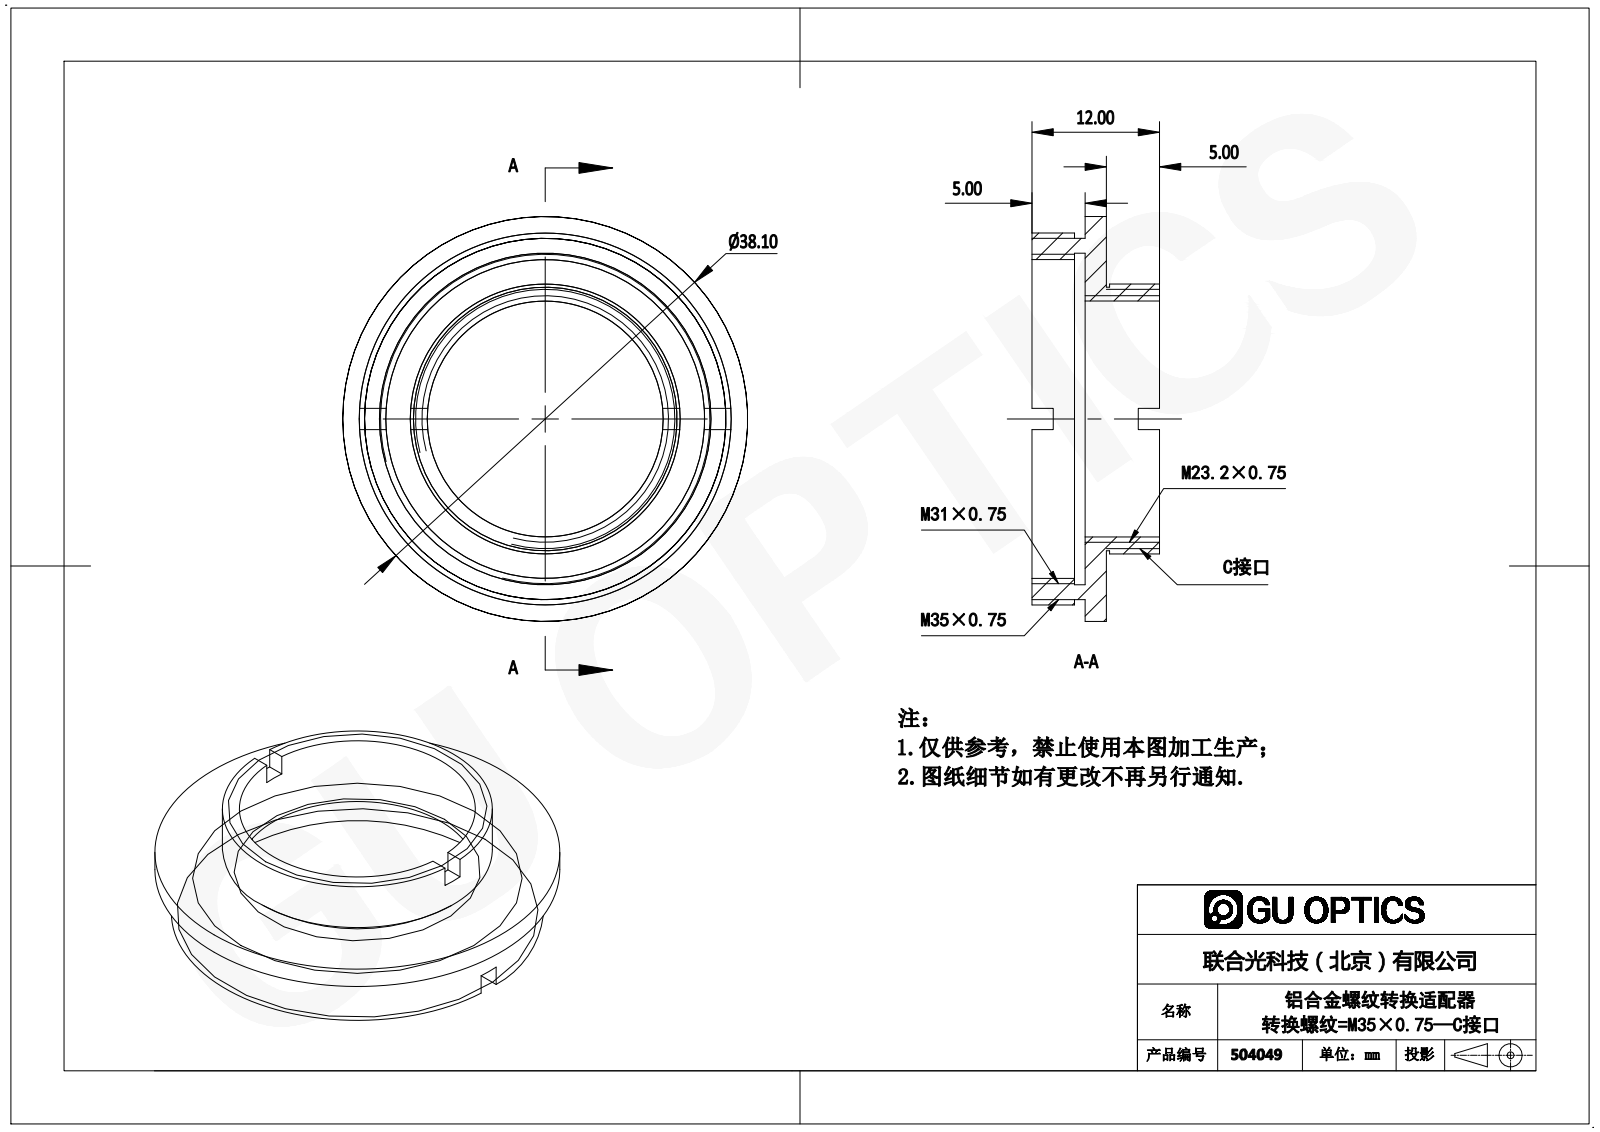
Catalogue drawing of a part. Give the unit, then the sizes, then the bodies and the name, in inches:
Units: inches
Overall size (bounding box): 1.5 × 1.5 × 0.472
Round holes (diameter × count): ⌀0.874 ×1, ⌀1.181 ×1, ⌀1.228 ×1
Round bosses / shafts (diameter × count): ⌀1.5 ×1, ⌀1.378 ×1, ⌀1.339 ×1, ⌀1 ×1, ⌀0.976 ×1
Main face-to-face distances: 0.079, 0.197, 0.276, 0.118, 0.315, 0.472, 0.157, 0.039, 0.287, 0.13
Volume: 0.197 in³ · Surface area: 6.085 in²
Bodies: 1 solid, 38 faces (22 planar, 16 cylindrical, 0 other)
Part name (STEP PRODUCT): 504049
STEP written by: SolidWorks 2016 (AUTOMOTIVE_DESIGN)
